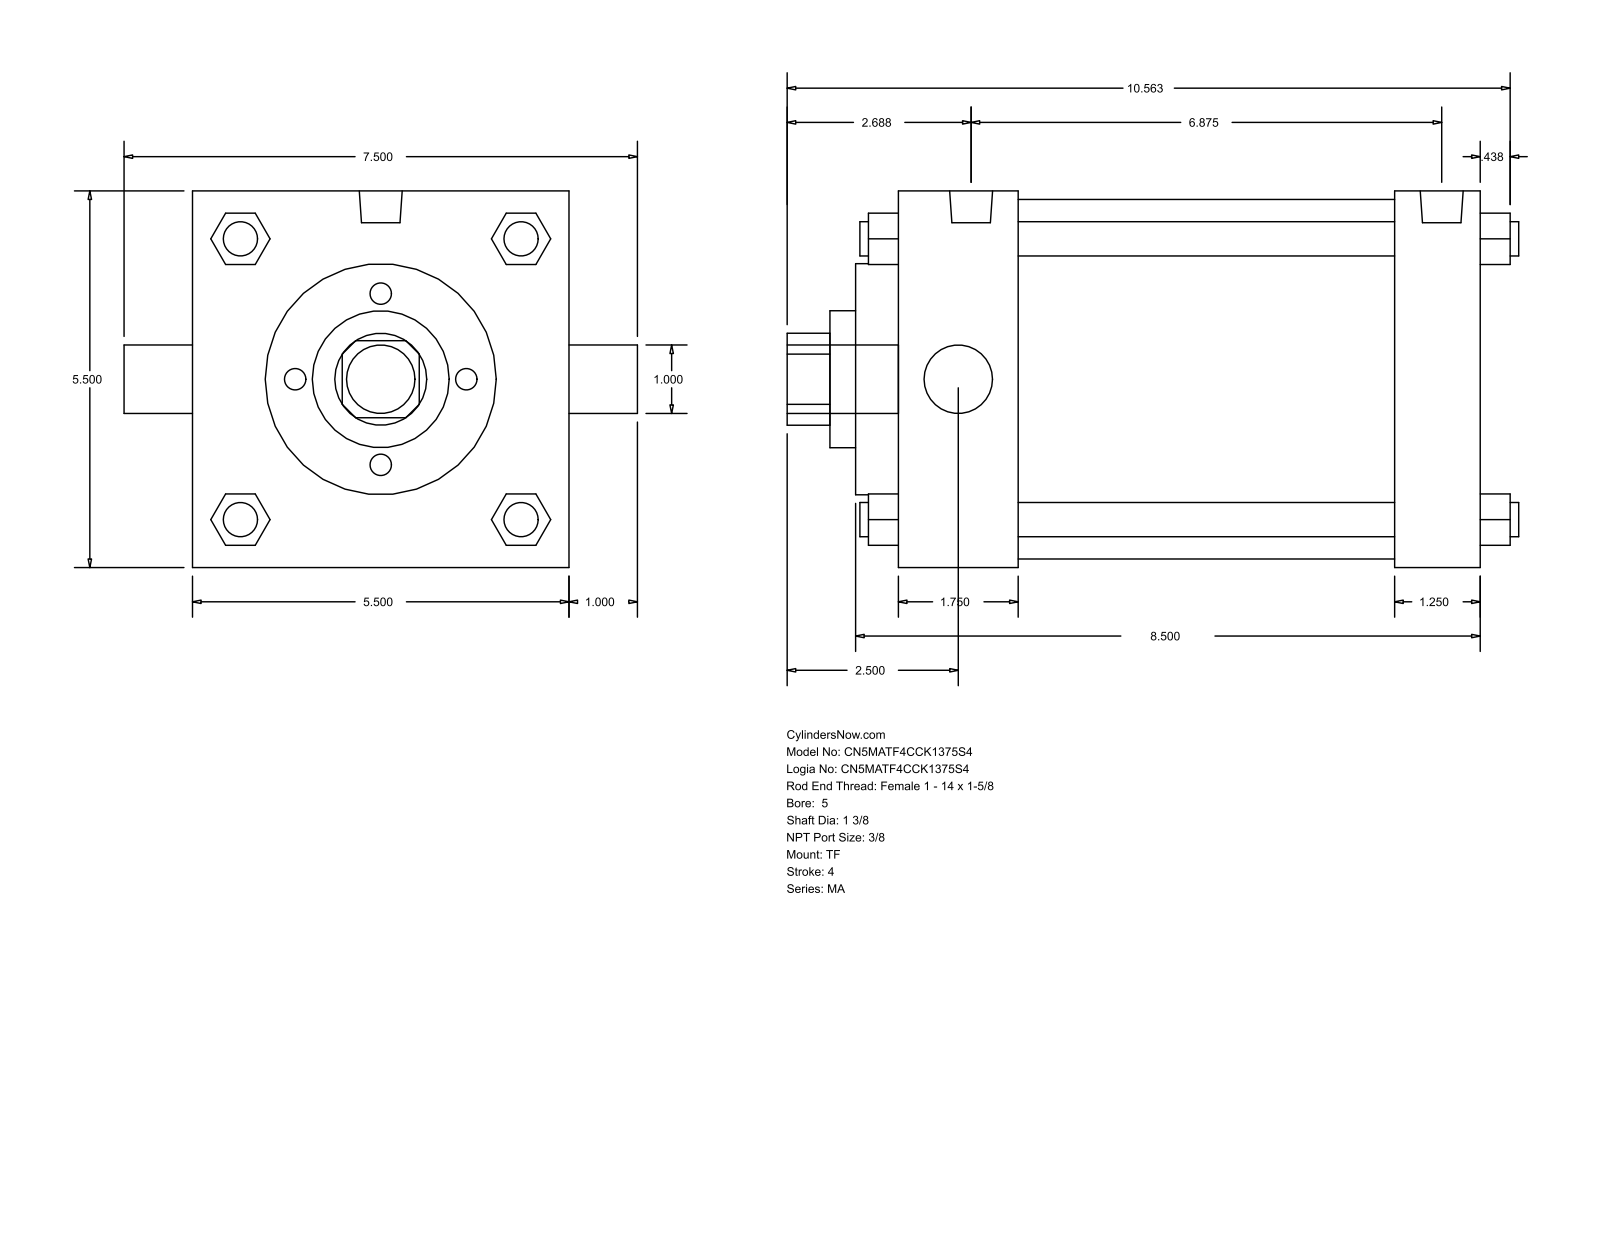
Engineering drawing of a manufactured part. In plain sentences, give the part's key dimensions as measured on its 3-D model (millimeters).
The part is named "MA_TF__0500_1.375". Its 3-D file was written by "GSSL Pune (CONFIG_CONTROL_DESIGN)". It is 0 solids with 122 faces: 93 planar, 29 cylindrical and 0 other. Overall it measures 271.46 by 190.5 by 139.7 millimeters. Round holes: 1 of diameter 25.4, 1 of diameter 34.92, 1 of diameter 50.8, 1 of diameter 85.72, 1 of diameter 133.35. Round bosses or shafts: 4 of diameter 12.7, 3 of diameter 11.11, 2 of diameter 15.93, 1 of diameter 25.4. Partial cylindrical surfaces (rounded edges, fillets, slot ends): 1 of radius 17.06. The main face-to-face distances are 139.7, 215.91, 184.16, 31.75, 44.45, 139.71, 171.46, 15.87, 60.32, 200.03.
